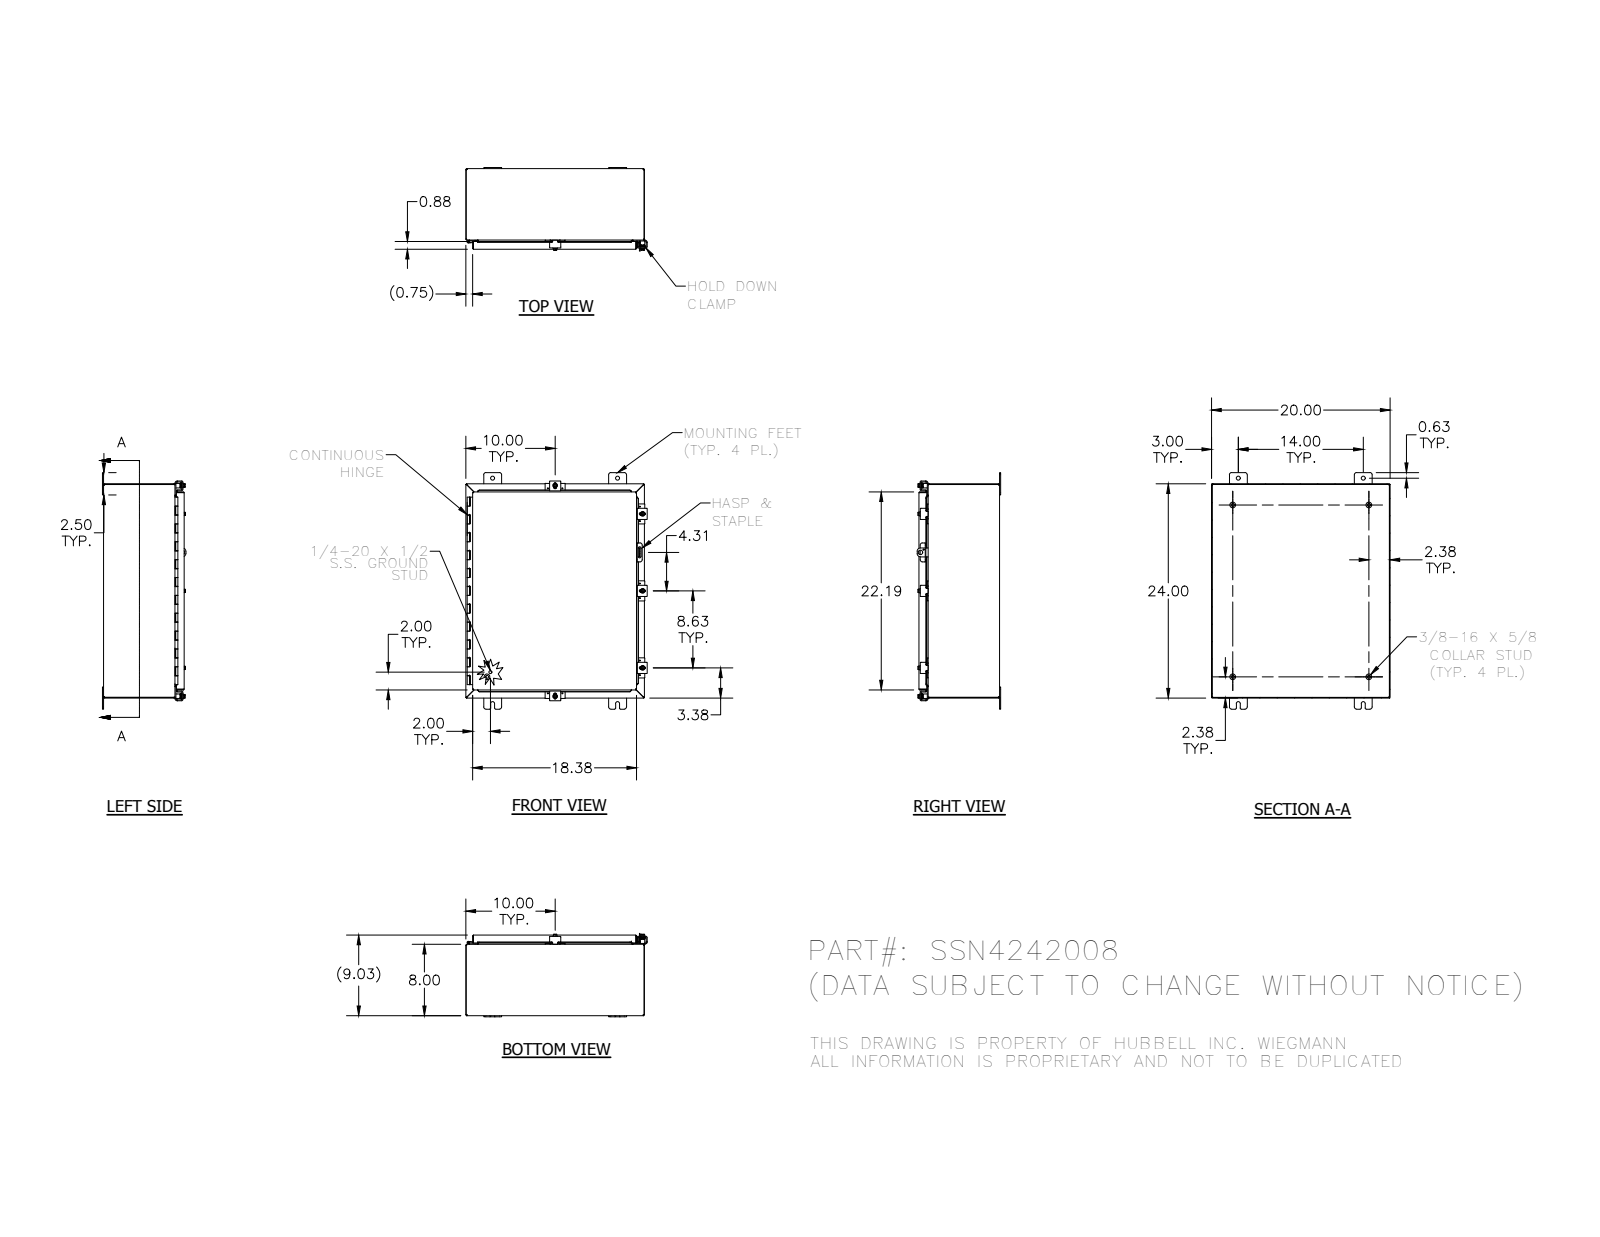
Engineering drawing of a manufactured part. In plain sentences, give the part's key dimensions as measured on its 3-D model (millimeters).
The part is named "SSN4242008; HFW30825-3_1; 328138_1; 30824-1_1 (+8 more)". Its 3-D file was written by "SolidWorks 2014 (AUTOMOTIVE_DESIGN)". It is 42 solids with 1674 faces: 650 planar, 737 cylindrical and 287 other. Overall it measures 673.1 by 515.9 by 237.6 millimeters. Its volume is 2 510 000 cubic millimeters and its surface area 2 591 000 square millimeters. Round holes: 10 of diameter 2.8, 5 of diameter 5.4, 5 of diameter 7.1, 5 of diameter 7.6, 4 of diameter 11.1, 1 of diameter 3.2, 1 of diameter 4, 1 of diameter 12.7. Round bosses or shafts: 7 of diameter 6.4, 5 of diameter 13.2, 5 of diameter 12.7, 5 of diameter 8.9, 4 of diameter 15.9, 4 of diameter 8.4, 2 of diameter 2.9, 1 of diameter 8.6. Partial cylindrical surfaces (rounded edges, fillets, slot ends): 61 of radius 0.8, 35 of radius 3.2, 31 of radius 6.4, 23 of radius 0.8, 23 of radius 2.7, 13 of radius 1.6, 10 of radius 3.6, 8 of radius 1.8. The main face-to-face distances are 1.9, 227.6, 225.7, 229.4, 506.1, 607.7, 201.3, 26.2, 504.2, 508. The hole center spacings are 22.3, 591.9, 41.3, 198.6, 219.1, 219.1, 239.9, 438.2.
